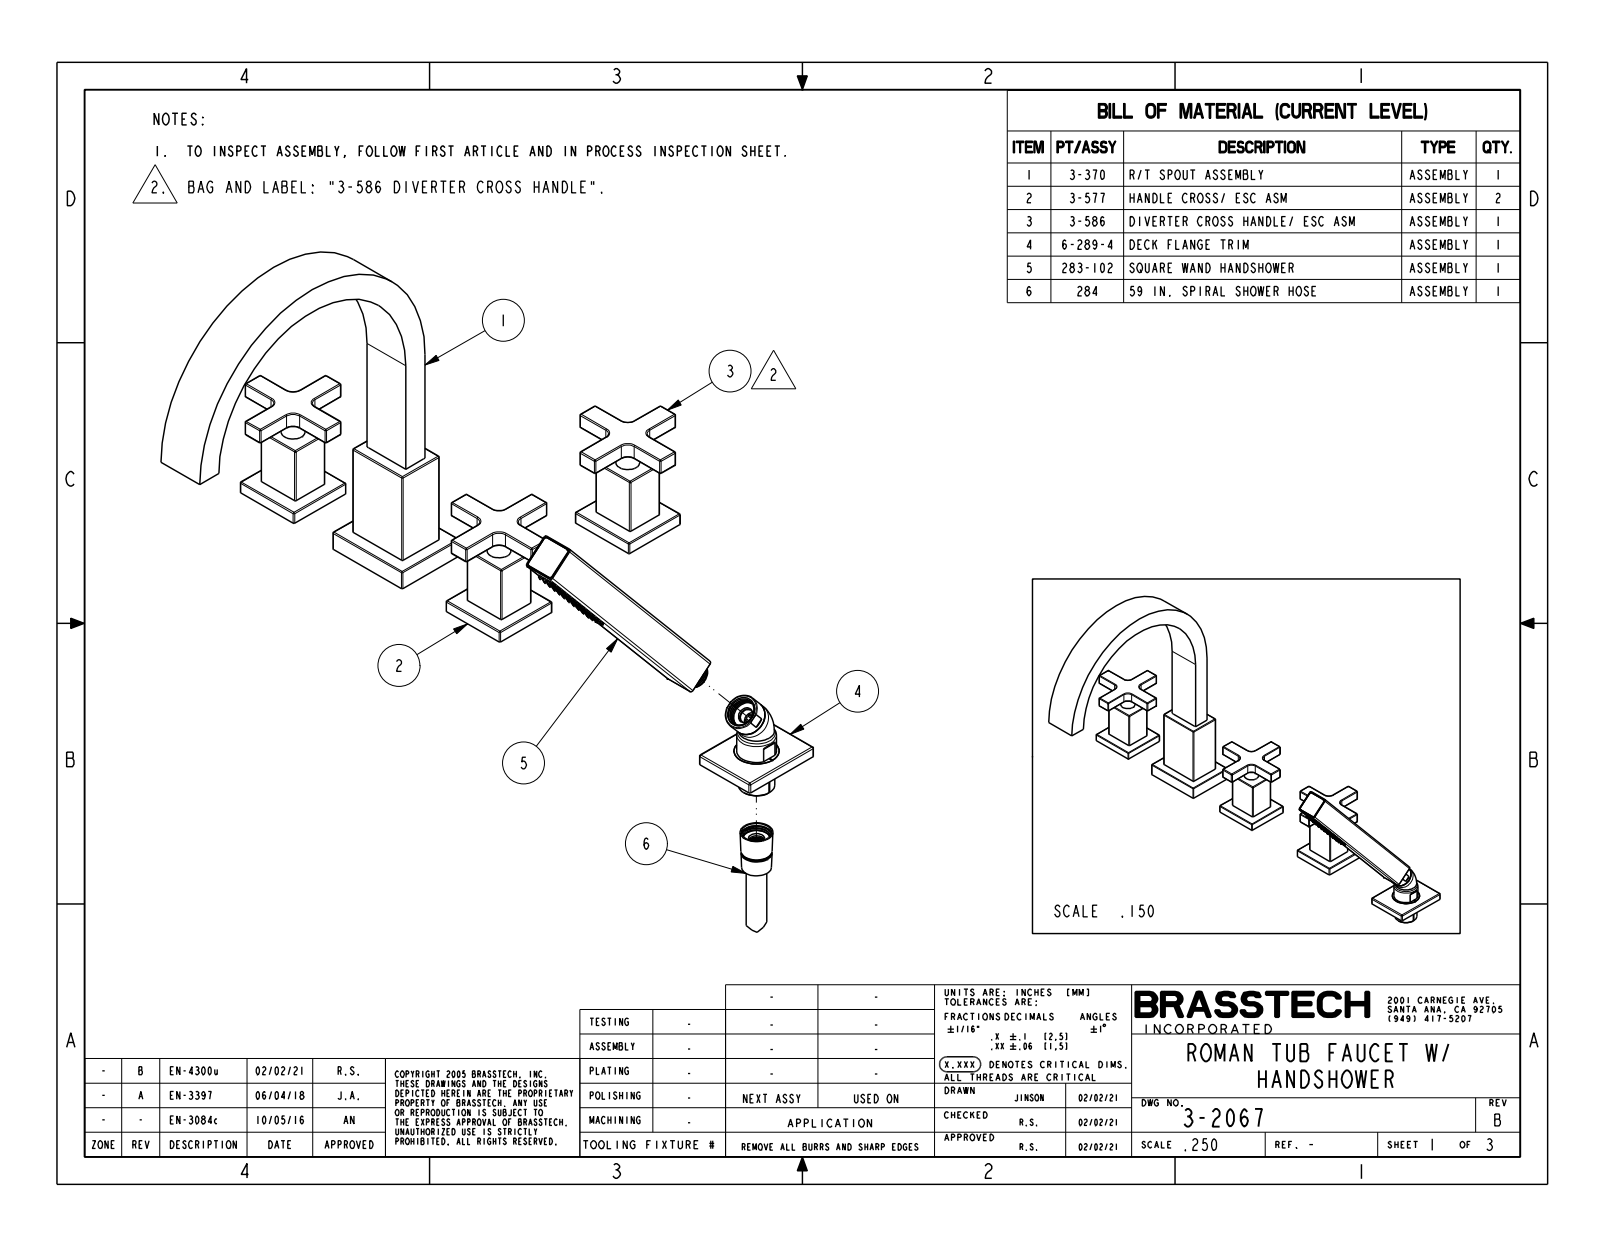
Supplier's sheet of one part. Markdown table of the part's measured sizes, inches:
| quantity | value |
| --- | --- |
| part name | 3-2067 |
| STEP written by | CREO PARAMETRIC BY PTC INC, 2018400 (CONFIG_CONTROL_DESIGN) |
| units | inches |
| bodies | 5 solids, 1186 faces (170 planar, 362 cylindrical, 654 other) |
| overall size | 20.555 × 11.224 × 9.945 |
| volume | 58.19 in³ |
| surface area | 260.1 in² |
| round holes (diameter × count) | 0.14 × 44, 0.835 × 1 |
| round bosses / shafts (diameter × count) | 0.65 × 3, 0.523 × 3, 1.095 × 1, 0.98 × 1, 0.975 × 1, 0.825 × 1 |
| partial cylindrical surfaces (radius × count) | 0.03 × 114, 0.01 × 16, 0.25 × 12, 0.04 × 8, 0.05 × 6, 0.065 × 4, 0.5 × 2, 3.625 × 1 |
| main face-to-face distances | 1.5, 1.3, 0.205, 0.955, 0.14, 0.345, 1.095, 3.046, 1.72, 2.596 |
| hole center spacings | 0.336, 0.17, 0.447, 0.672, 0.604, 0.29, 0.87, 0.887 |
